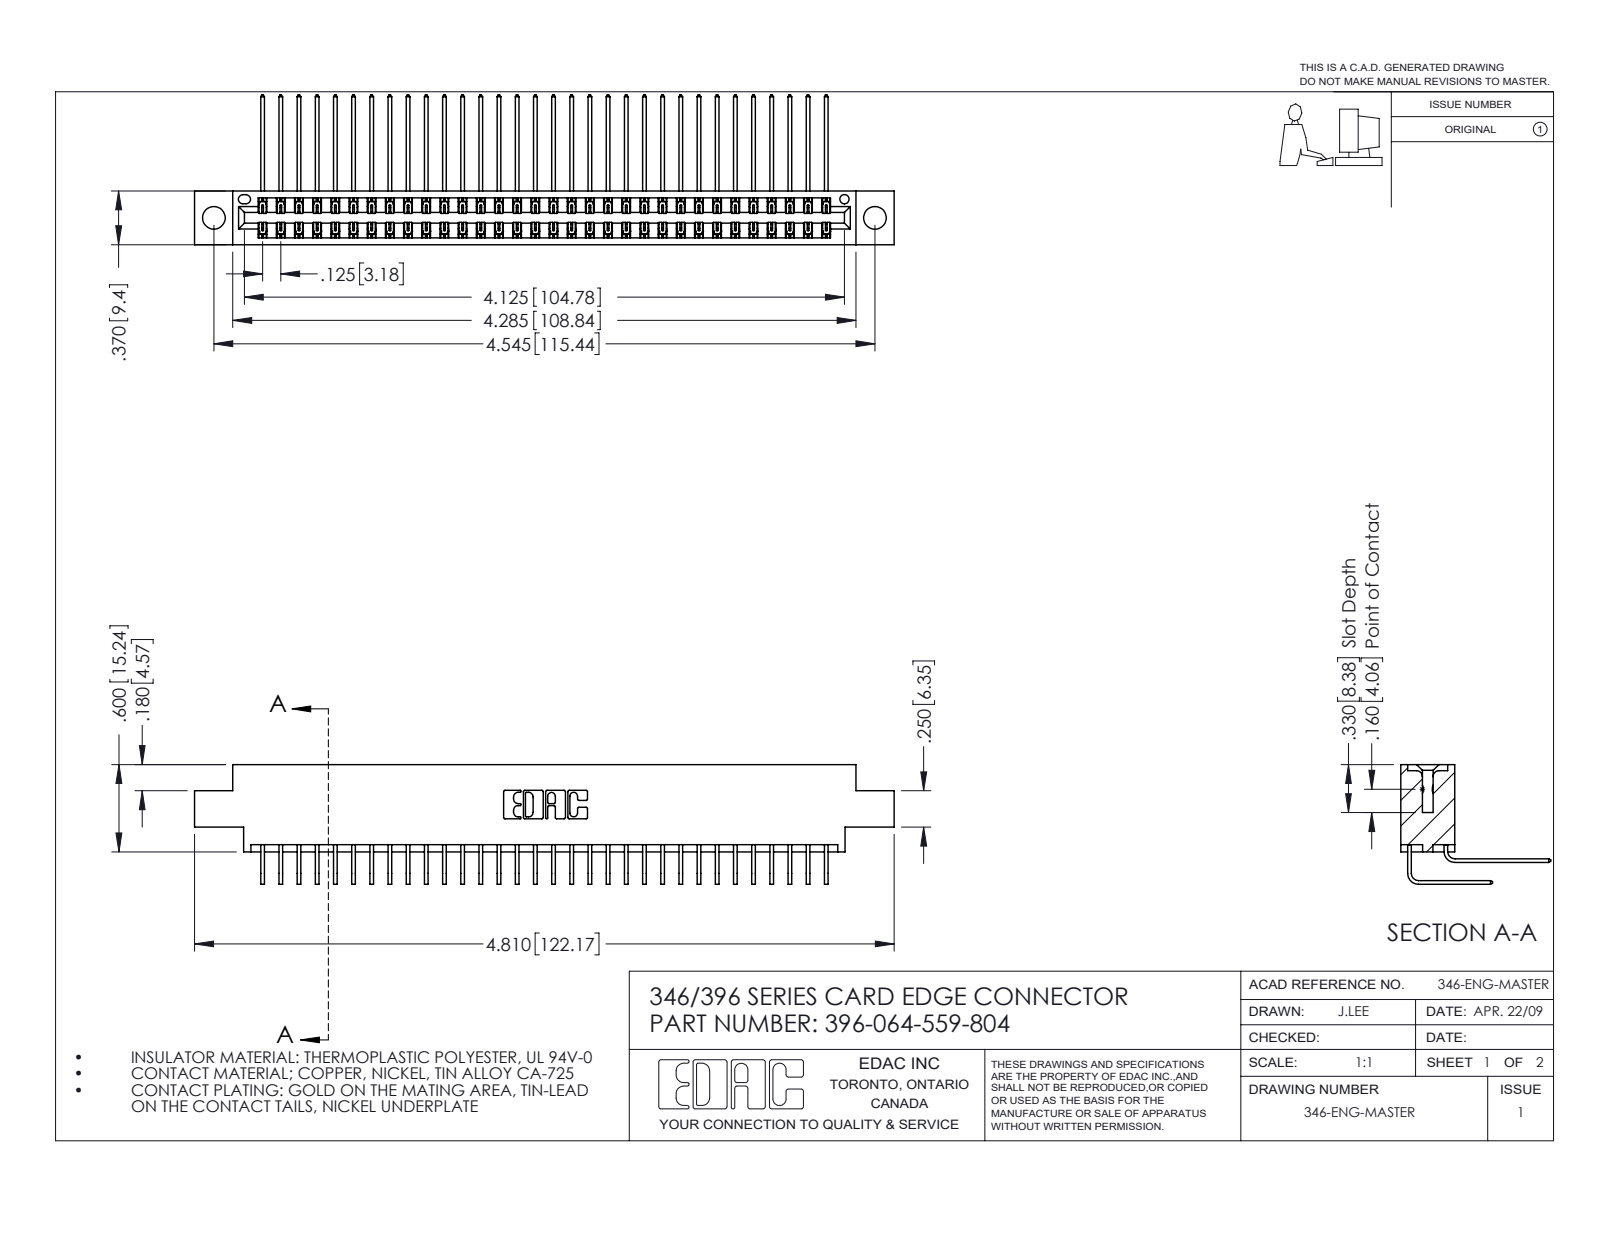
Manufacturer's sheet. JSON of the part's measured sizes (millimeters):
{"part_name": "345-292-001_559 Tail - 2; 396-064-559-804; 345-292-001_558 559 Tail - 1; 346 Part_0.170 Offset - 0.156 Dia-TH", "step_written_by": "SolidWorks 2016 (CONFIG_CONTROL_DESIGN)", "units": "millimeters", "bodies": {"solids": 65, "faces": 3582, "planar": 2448, "cylindrical": 1134, "other": 0}, "overall_size": [122.2, 26.2, 20.9], "volume_mm3": 12000, "surface_area_mm2": 18050, "round_holes": [[4, 2], [1.6, 1]], "partial_cylinders_radius": [[0.2, 96], [0.3, 22], [0.2, 6], [0.8, 6], [0.7, 3], [0.4, 2], [0.6, 2], [0.6, 2]], "face_to_face_distances": [1.2, 8.2, 0.6, 9.4, 6.4, 1.8, 7.6, 7, 3.8, 5.6], "hole_center_spacings": [6.2, 110.2, 115.4]}
